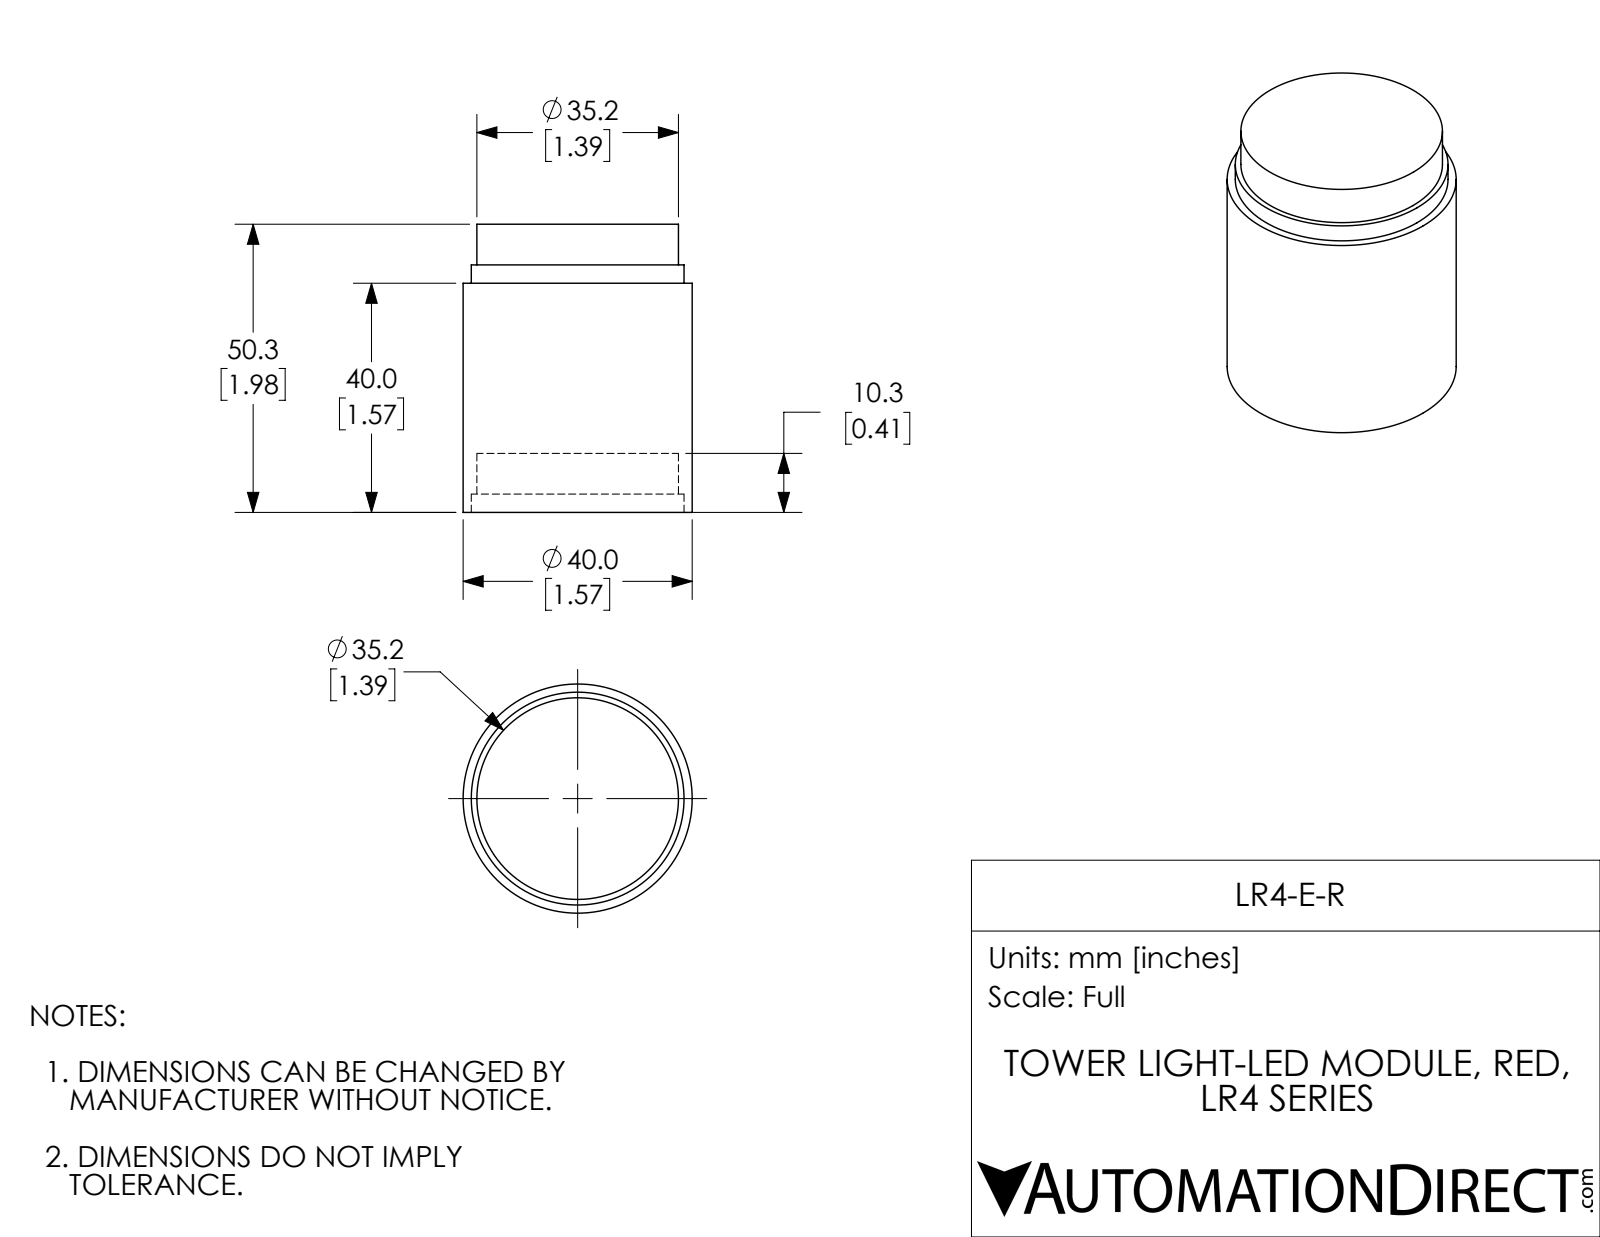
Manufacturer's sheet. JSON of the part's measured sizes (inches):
{"part_name": "LR4-E-R", "step_written_by": "SolidWorks 2017 (AUTOMOTIVE_DESIGN)", "units": "inches", "bodies": {"solids": 1, "faces": 16, "planar": 6, "cylindrical": 10, "other": 0}, "overall_size": [1.98, 1.575, 1.575], "volume_in3": 3.067, "surface_area_in2": 15.28, "round_holes": [[1.386, 1], [1.463, 1]], "round_bosses_or_shafts": [[1.575, 1]], "face_to_face_distances": [1.575, 0.406, 0.126, 0.28, 1.98, 1.169, 1.701, 1.295, 1.449, 1.854]}
